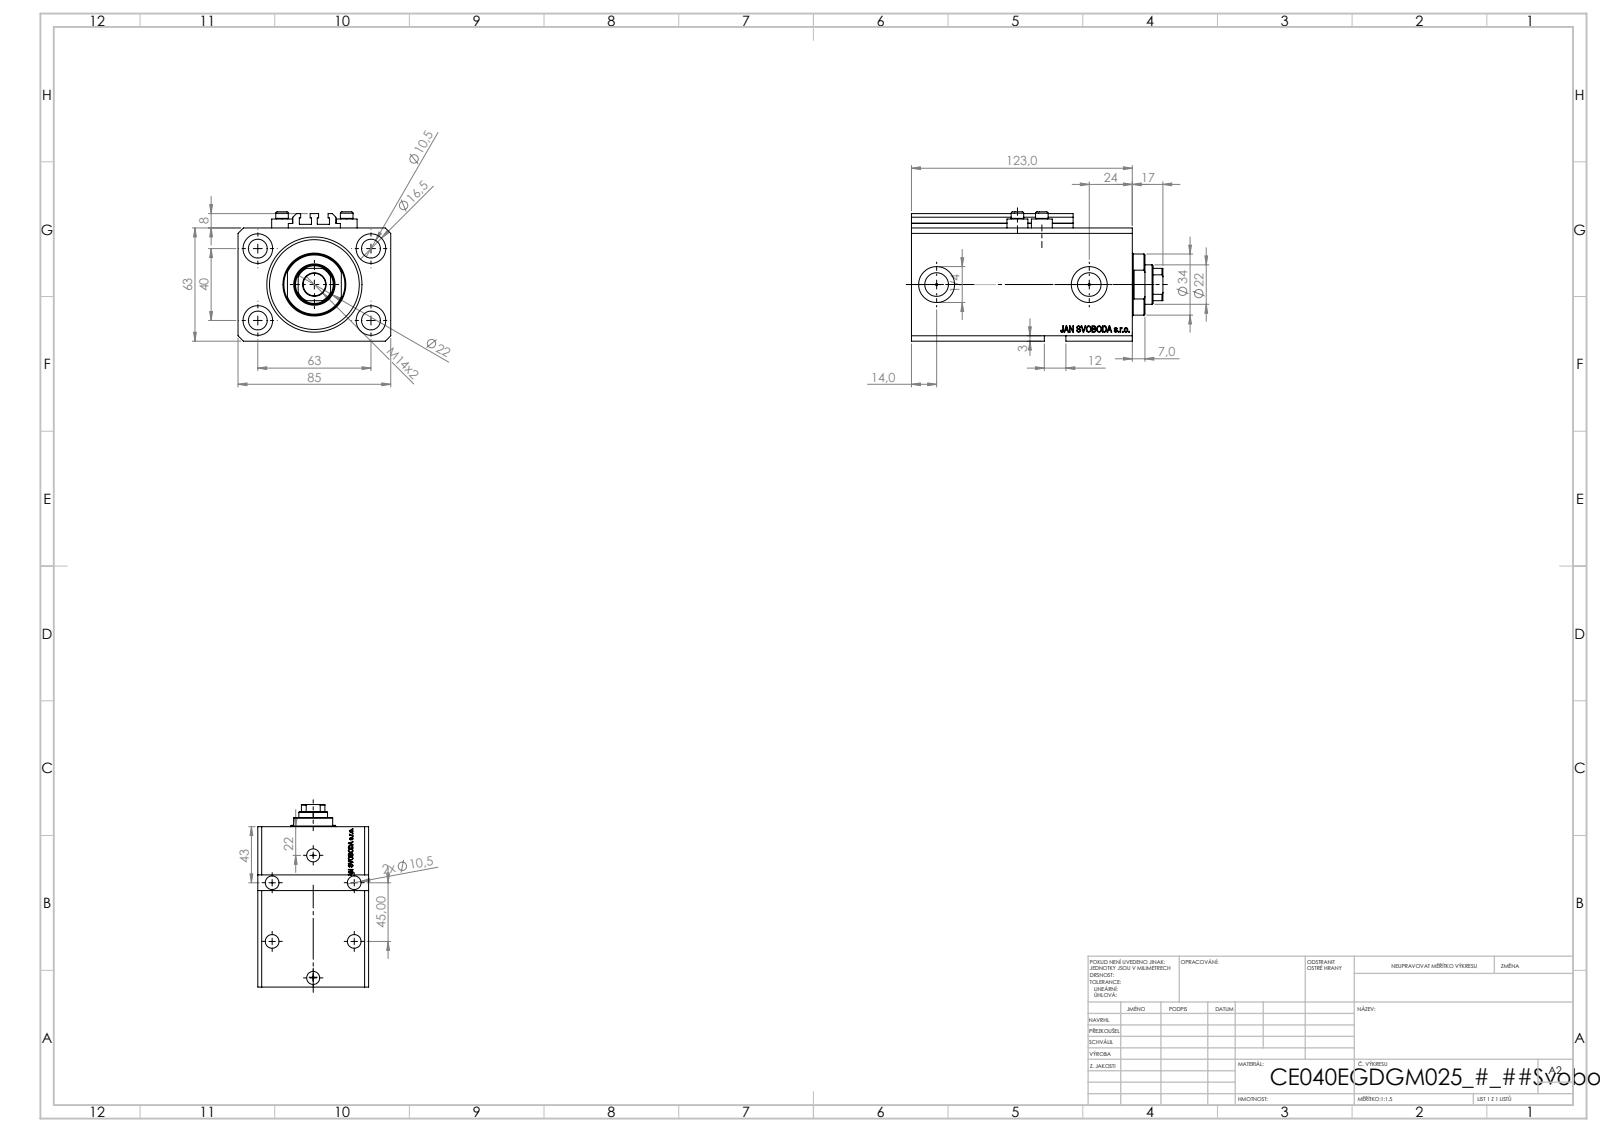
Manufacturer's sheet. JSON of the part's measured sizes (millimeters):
{"part_name": "ALLEN BOLT V250CE; V250CE_C_VCP; V250CE_E_Body; V250CE_VC_E", "step_written_by": "SolidWorks 2019 (CONFIG_CONTROL_DESIGN)", "units": "millimeters", "bodies": {"solids": 8, "faces": 1123, "planar": 539, "cylindrical": 158, "other": 426}, "overall_size": [140, 85, 72], "volume_mm3": 553016, "surface_area_mm2": 120484, "round_holes": [[10.5, 8], [1.25, 4], [4, 4], [16.5, 4], [10, 2], [13.16, 2], [20, 2], [12.5, 1], [22, 1], [40, 1], [53, 1]], "round_bosses_or_shafts": [[11.6, 4], [7, 4], [34, 1]], "partial_cylinders_radius": [[0.2, 10], [10.5, 1]], "face_to_face_distances": [63, 85, 123, 17, 106, 11.4, 94.6, 111.6, 3, 56], "hole_center_spacings": [37.31, 63, 13.6, 15.4, 24.96, 27.54, 33.62, 36]}
